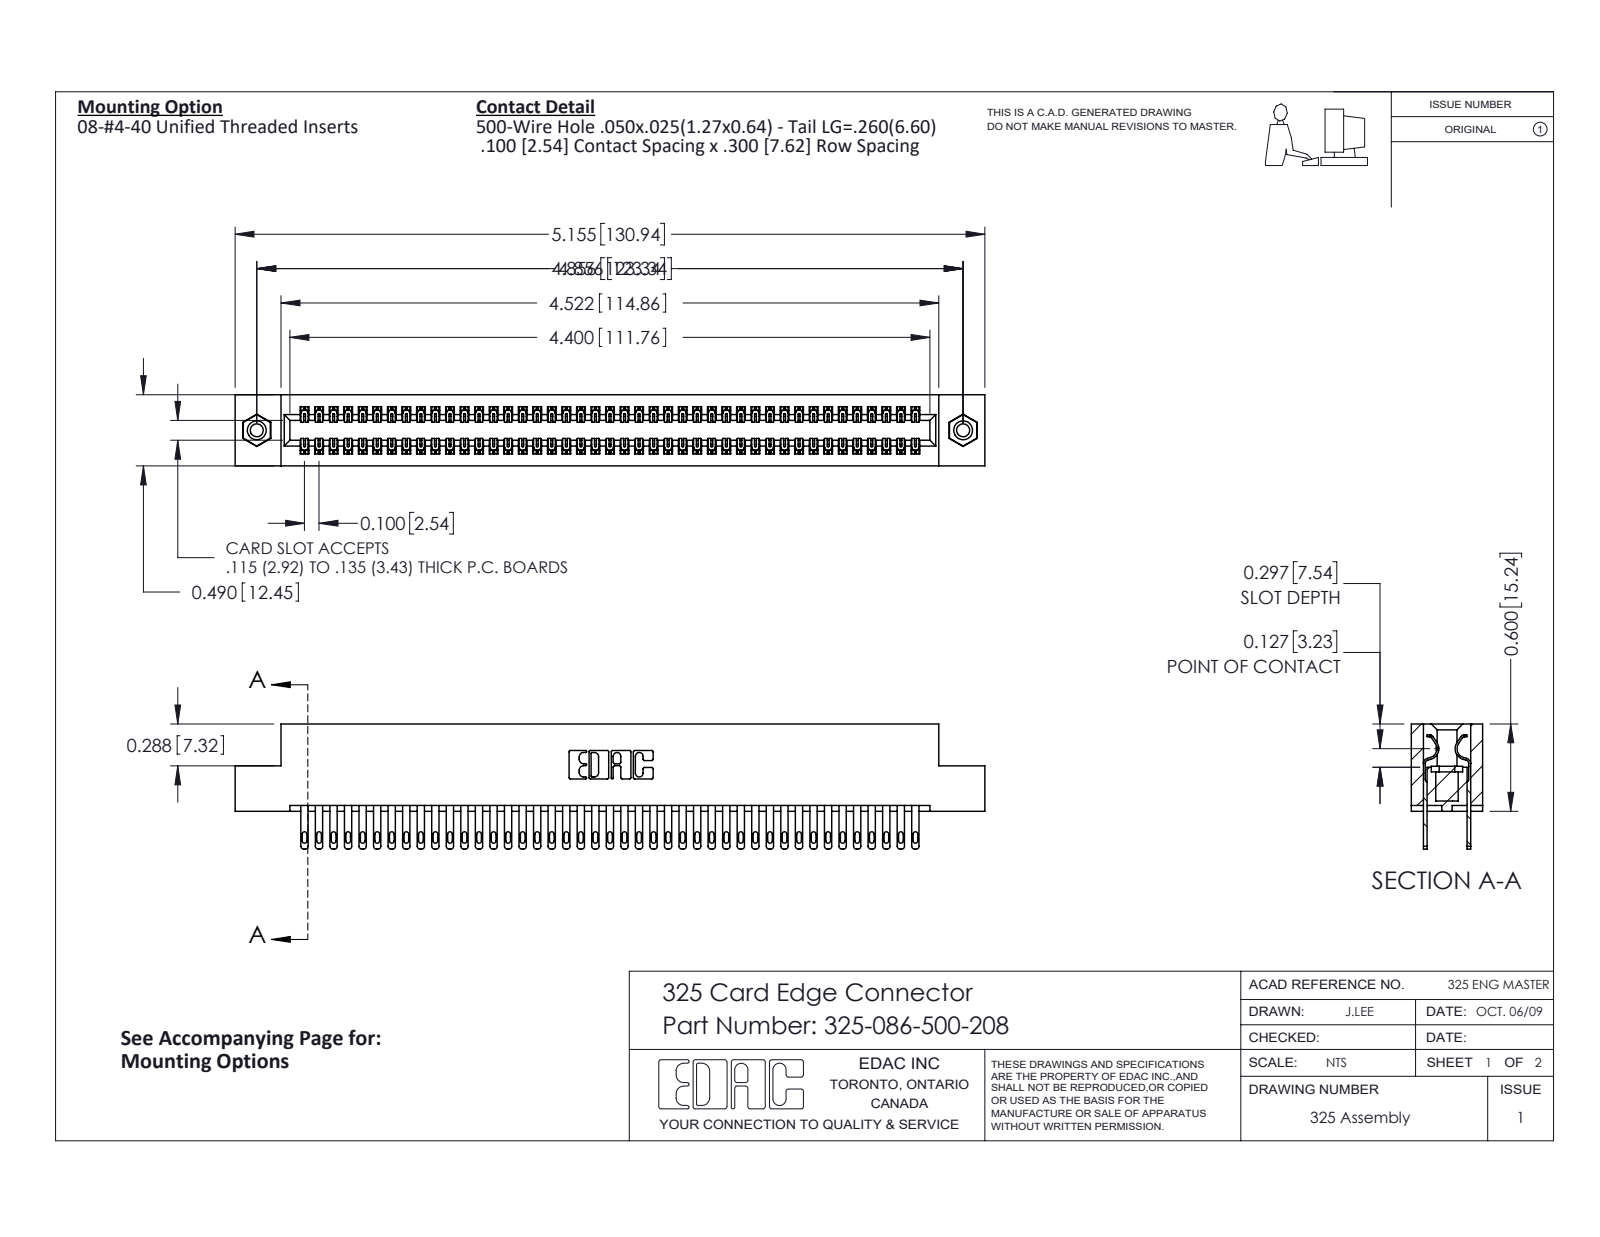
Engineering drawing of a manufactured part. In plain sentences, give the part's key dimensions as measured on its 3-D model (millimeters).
The part is named "325-086-500-208; 325 Part_TI; 345-250-001_345-250-003-102; 325-292-001_325-293-100". Its 3-D file was written by "SolidWorks 2016 (CONFIG_CONTROL_DESIGN)". It is 89 solids with 4302 faces: 2682 planar, 1604 cylindrical and 16 other. Overall it measures 130.9 by 21.8 by 12.4 millimeters. Its volume is 17 170 cubic millimeters and its surface area 21 720 square millimeters. Round holes: 2 of diameter 2.3, 2 of diameter 3.2, 2 of diameter 4.1. Round bosses or shafts: 2 of diameter 3.9. Partial cylindrical surfaces (rounded edges, fillets, slot ends): 129 of radius 0.2, 86 of radius 0.4, 86 of radius 0.5, 22 of radius 0.3, 6 of radius 0.2, 6 of radius 0.8, 3 of radius 0.7, 2 of radius 0.4. The main face-to-face distances are 2.1, 10.3, 7.6, 2.7, 9.7, 0.6, 12.4, 8.3, 7, 14.2. The hole center spacings are 123.3.
